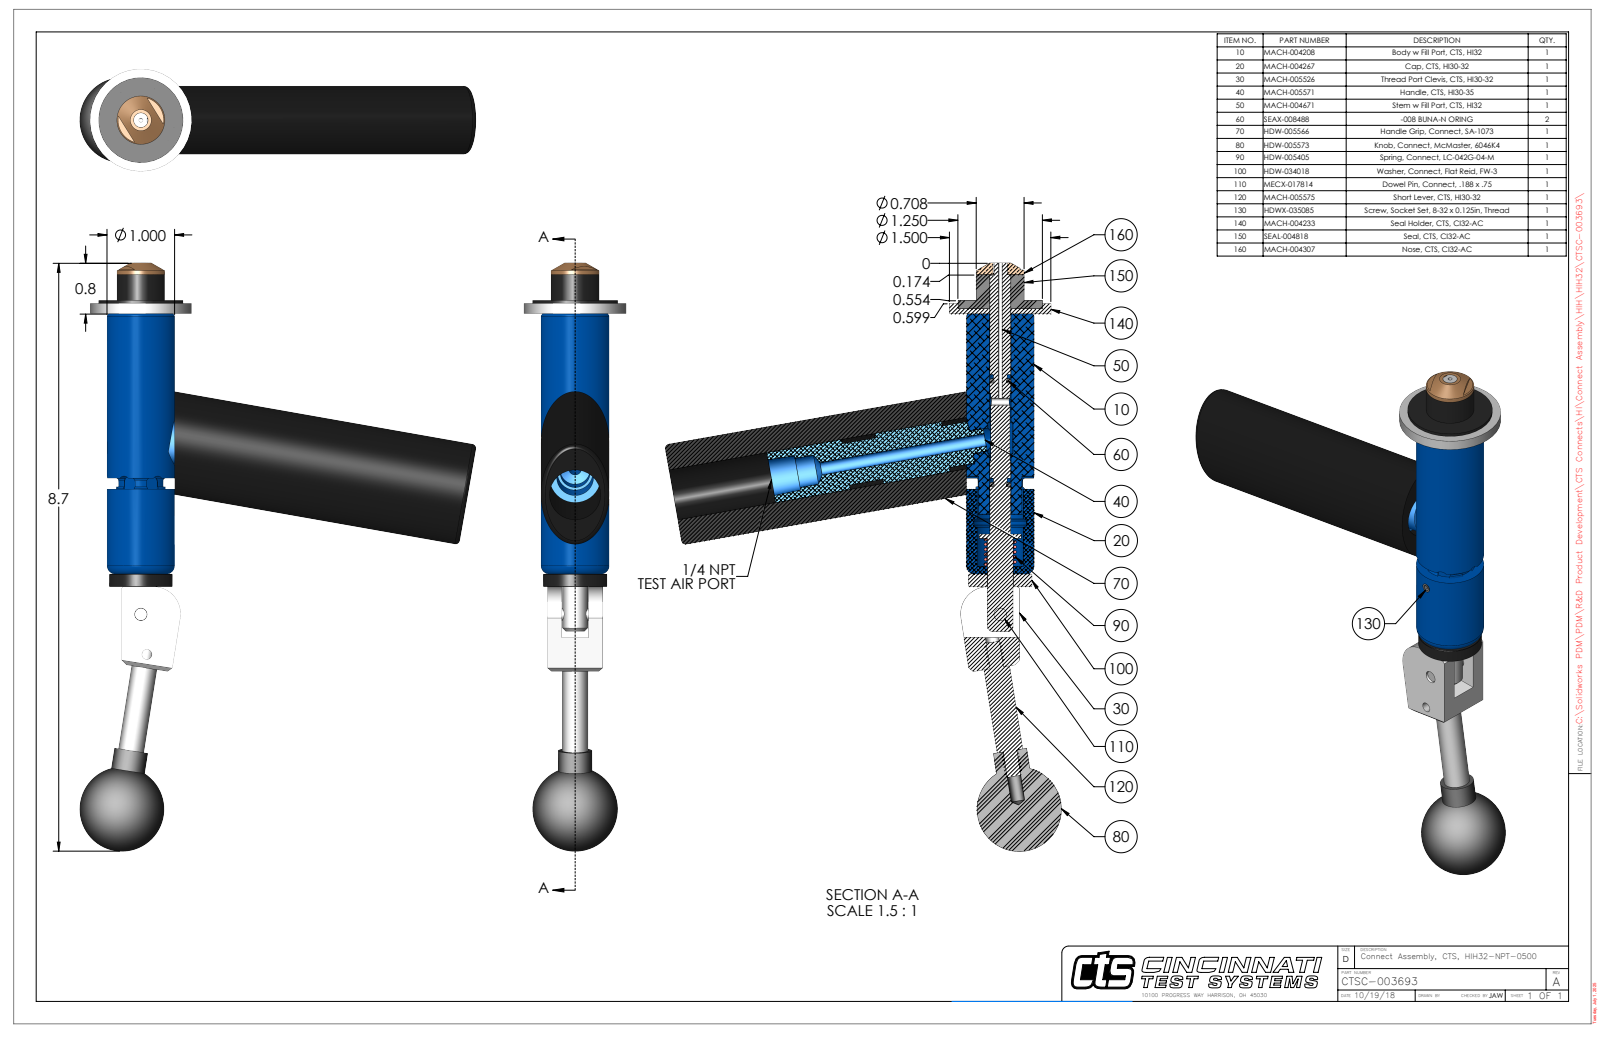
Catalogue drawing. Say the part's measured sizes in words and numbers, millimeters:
The part is named "CTSC-003693". Its 3-D file was written by "SolidWorks 2023 (AUTOMOTIVE_DESIGN)". It is 10 solids with 324 faces: 123 planar, 132 cylindrical and 69 other. Overall it measures 220.8 by 148.7 by 38.1 millimeters. Its volume is 158 400 cubic millimeters and its surface area 53 120 square millimeters. Round holes: 2 of diameter 5.1, 1 of diameter 1.6, 1 of diameter 2.8, 1 of diameter 2.8, 1 of diameter 3.5, 1 of diameter 3.8, 1 of diameter 4.7, 1 of diameter 4.8, 1 of diameter 5.4, 1 of diameter 7.9, 1 of diameter 8, 1 of diameter 8. Round bosses or shafts: 2 of diameter 6.4, 2 of diameter 5.1, 1 of diameter 38.1, 1 of diameter 25.4, 1 of diameter 23.8, 1 of diameter 19.1, 1 of diameter 18, 1 of diameter 15.7. Partial cylindrical surfaces (rounded edges, fillets, slot ends): 6 of radius 2.4, 2 of radius 0.7, 1 of radius 8.3, 1 of radius 9.5, 1 of radius 10.2, 1 of radius 11.4. The main face-to-face distances are 1.8, 5.3, 15.3, 99.5, 97.6, 20.6, 3.2, 5, 102.6, 9.7. The hole center spacings are 15.2, 42.1, 57.2.
